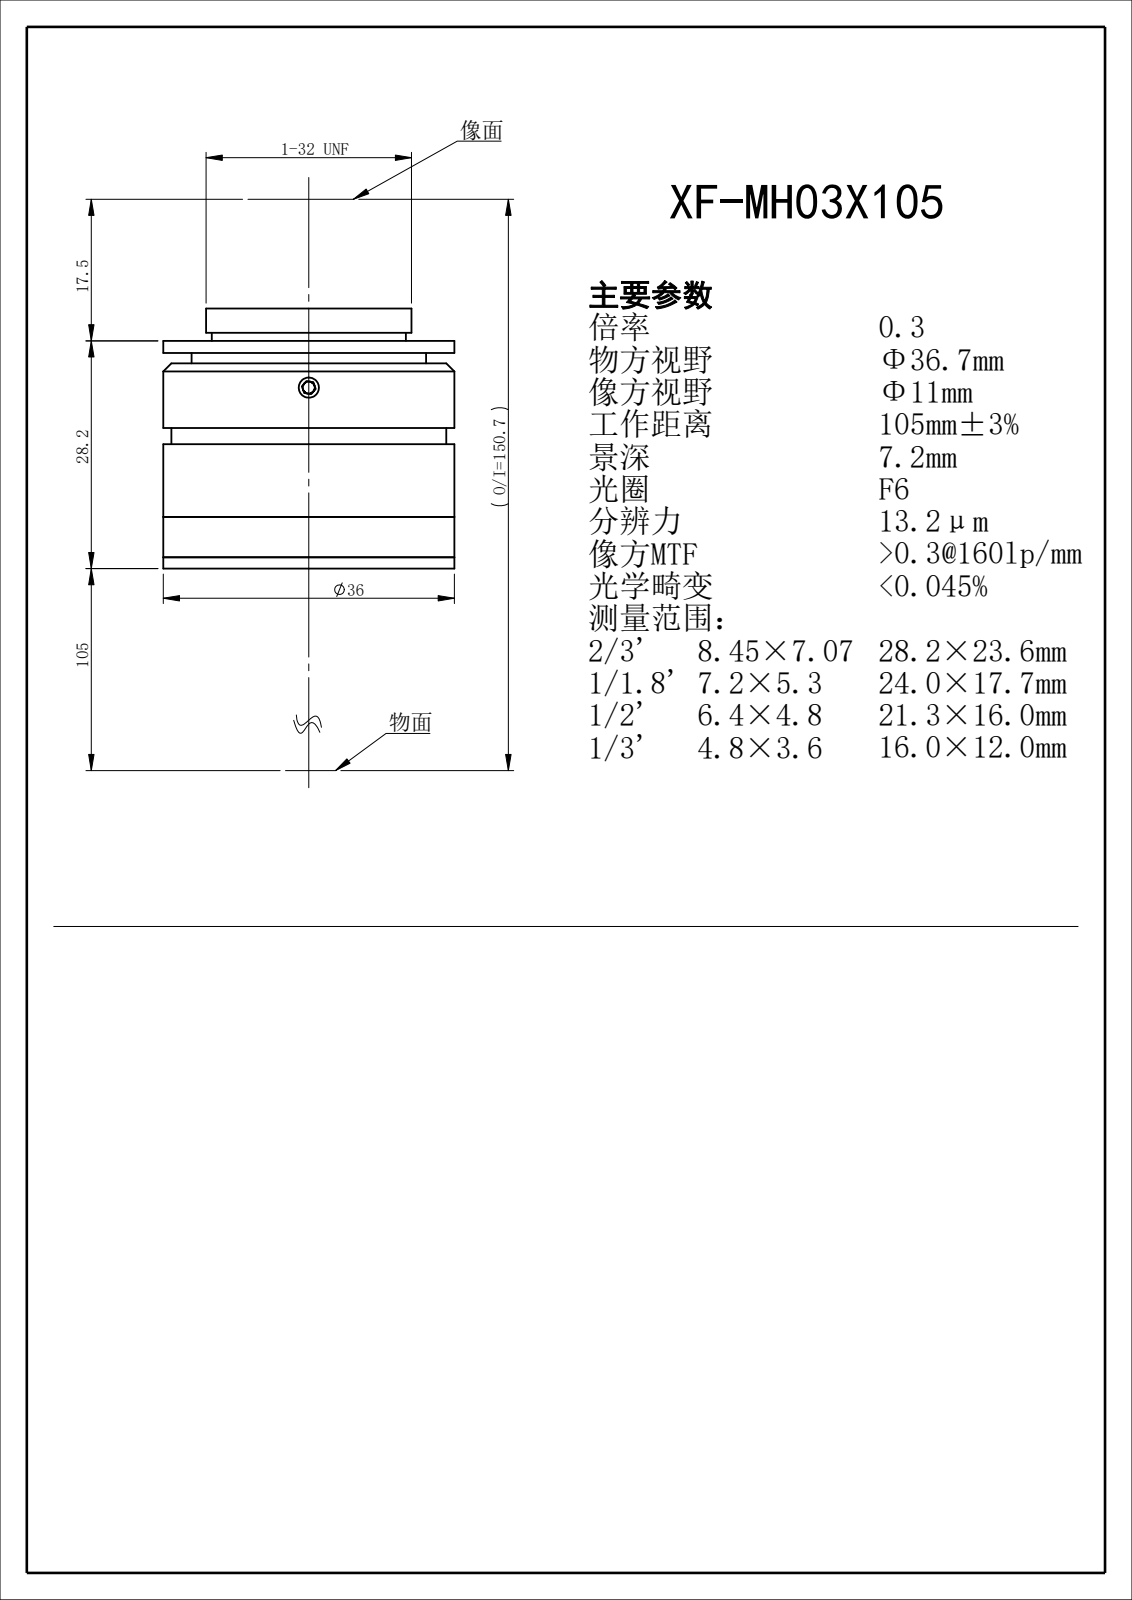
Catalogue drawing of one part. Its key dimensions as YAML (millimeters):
part_name: "XF-MH03X105"
step_written_by: "SolidWorks 2022 (CONFIG_CONTROL_DESIGN)"
units: millimeters
bodies: {solids: 0, faces: 100, planar: 48, cylindrical: 40, other: 12}
overall_size: [36, 36, 32.19]
round_holes:
  - {diameter: 2.5, count: 3}
  - {diameter: 8, count: 1}
  - {diameter: 9, count: 1}
  - {diameter: 10.4, count: 1}
  - {diameter: 13, count: 1}
  - {diameter: 17, count: 1}
  - {diameter: 21, count: 1}
  - {diameter: 21.5, count: 1}
  - {diameter: 24.9, count: 1}
  - {diameter: 26, count: 1}
round_bosses_or_shafts:
  - {diameter: 36, count: 1}
  - {diameter: 34, count: 1}
  - {diameter: 25.4, count: 1}
  - {diameter: 24, count: 1}
face_to_face_distances: [5, 26.79, 21.79, 1.4, 6.4, 28.19, 26.69, 1.5, 25.29, 20.29]
